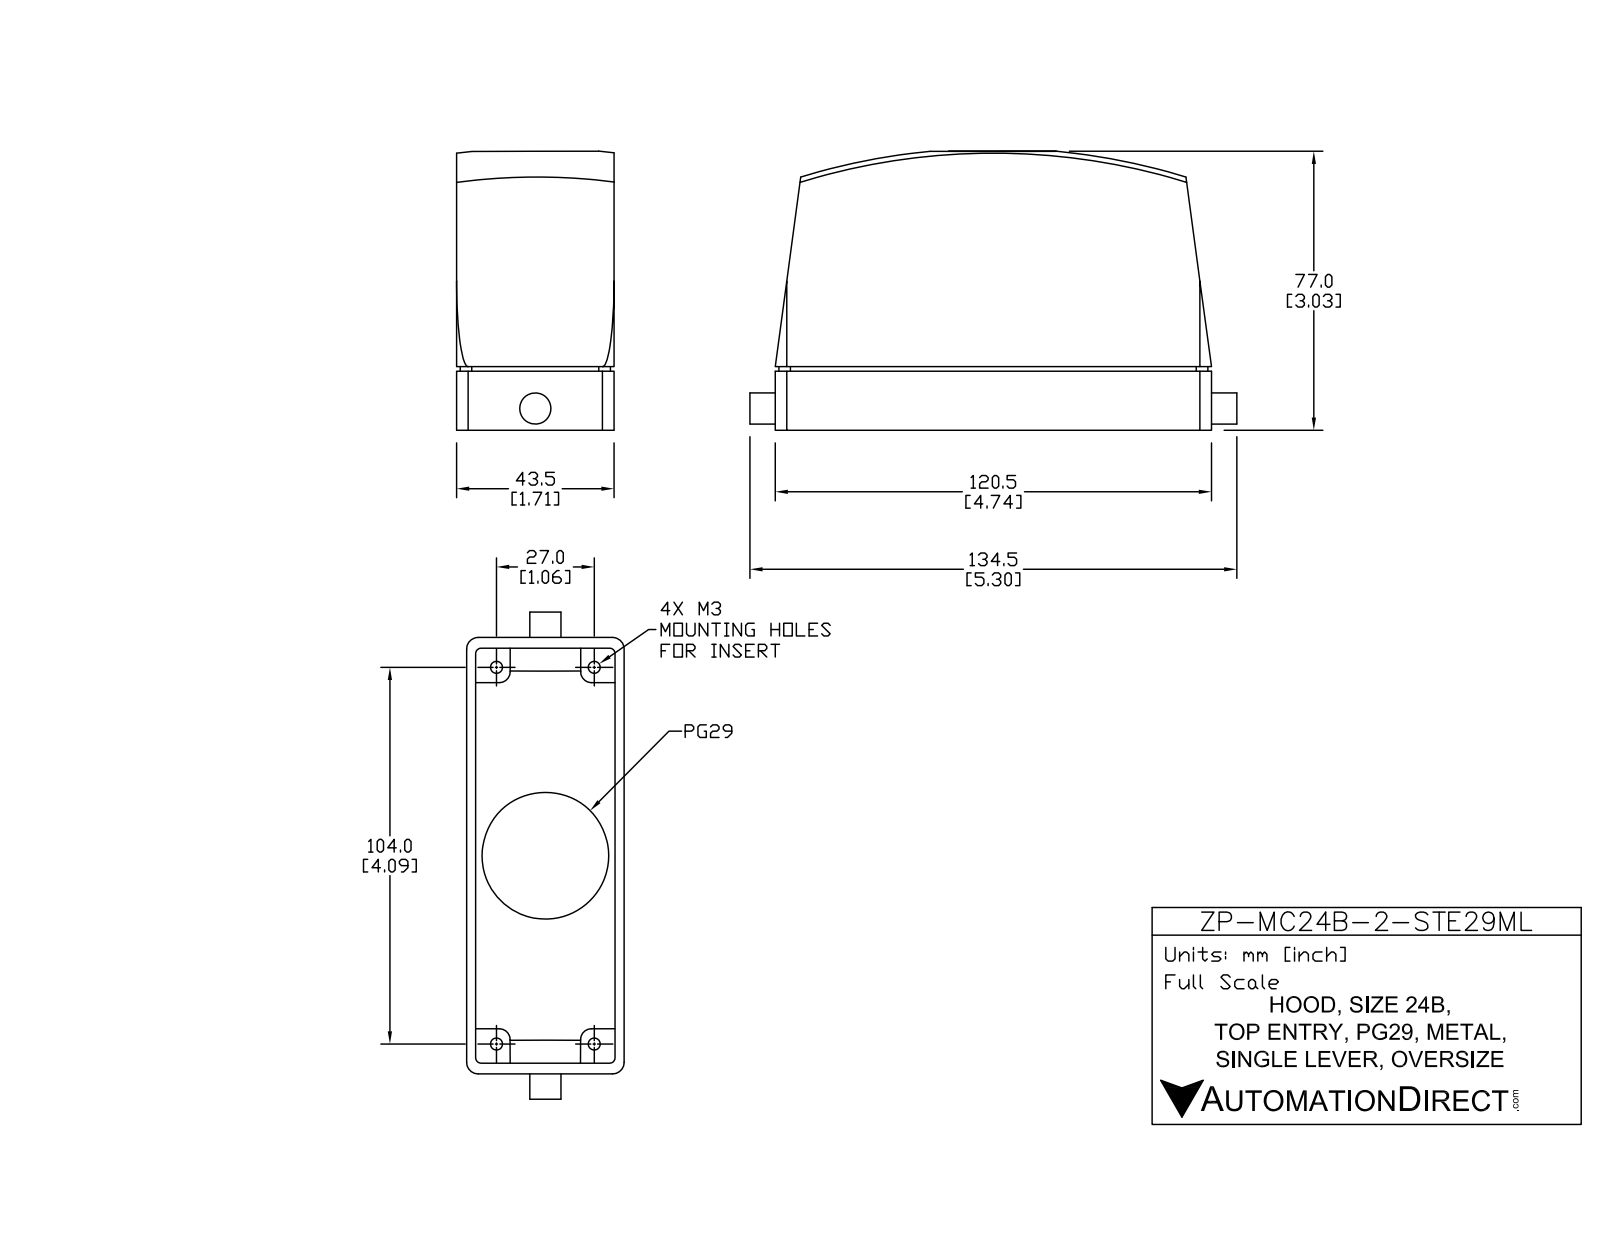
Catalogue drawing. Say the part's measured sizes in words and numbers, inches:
The part is named "ZP-MC24B-2-STE29ML". Its 3-D file was written by "SolidWorks 2011 (AUTOMOTIVE_DESIGN)". It is 5 solids with 86 faces: 52 planar, 28 cylindrical and 6 other. Overall it measures 5.295 by 3.021 by 1.713 inches. Its volume is 4.818 cubic inches and its surface area 94.32 square inches. Round holes: 4 of diameter 0.13, 1 of diameter 1.378. Round bosses or shafts: 1 of diameter 0.339. Partial cylindrical surfaces (rounded edges, fillets, slot ends): 8 of radius 0.126, 4 of radius 0.059, 4 of radius 0.118, 1 of radius 0.028. The main face-to-face distances are 0.098, 1.614, 1.713, 1.516, 0.374, 4.137, 0.117, 0.491, 4.254, 4.628. The hole center spacings are 2.115, 1.063, 4.094, 4.23.
